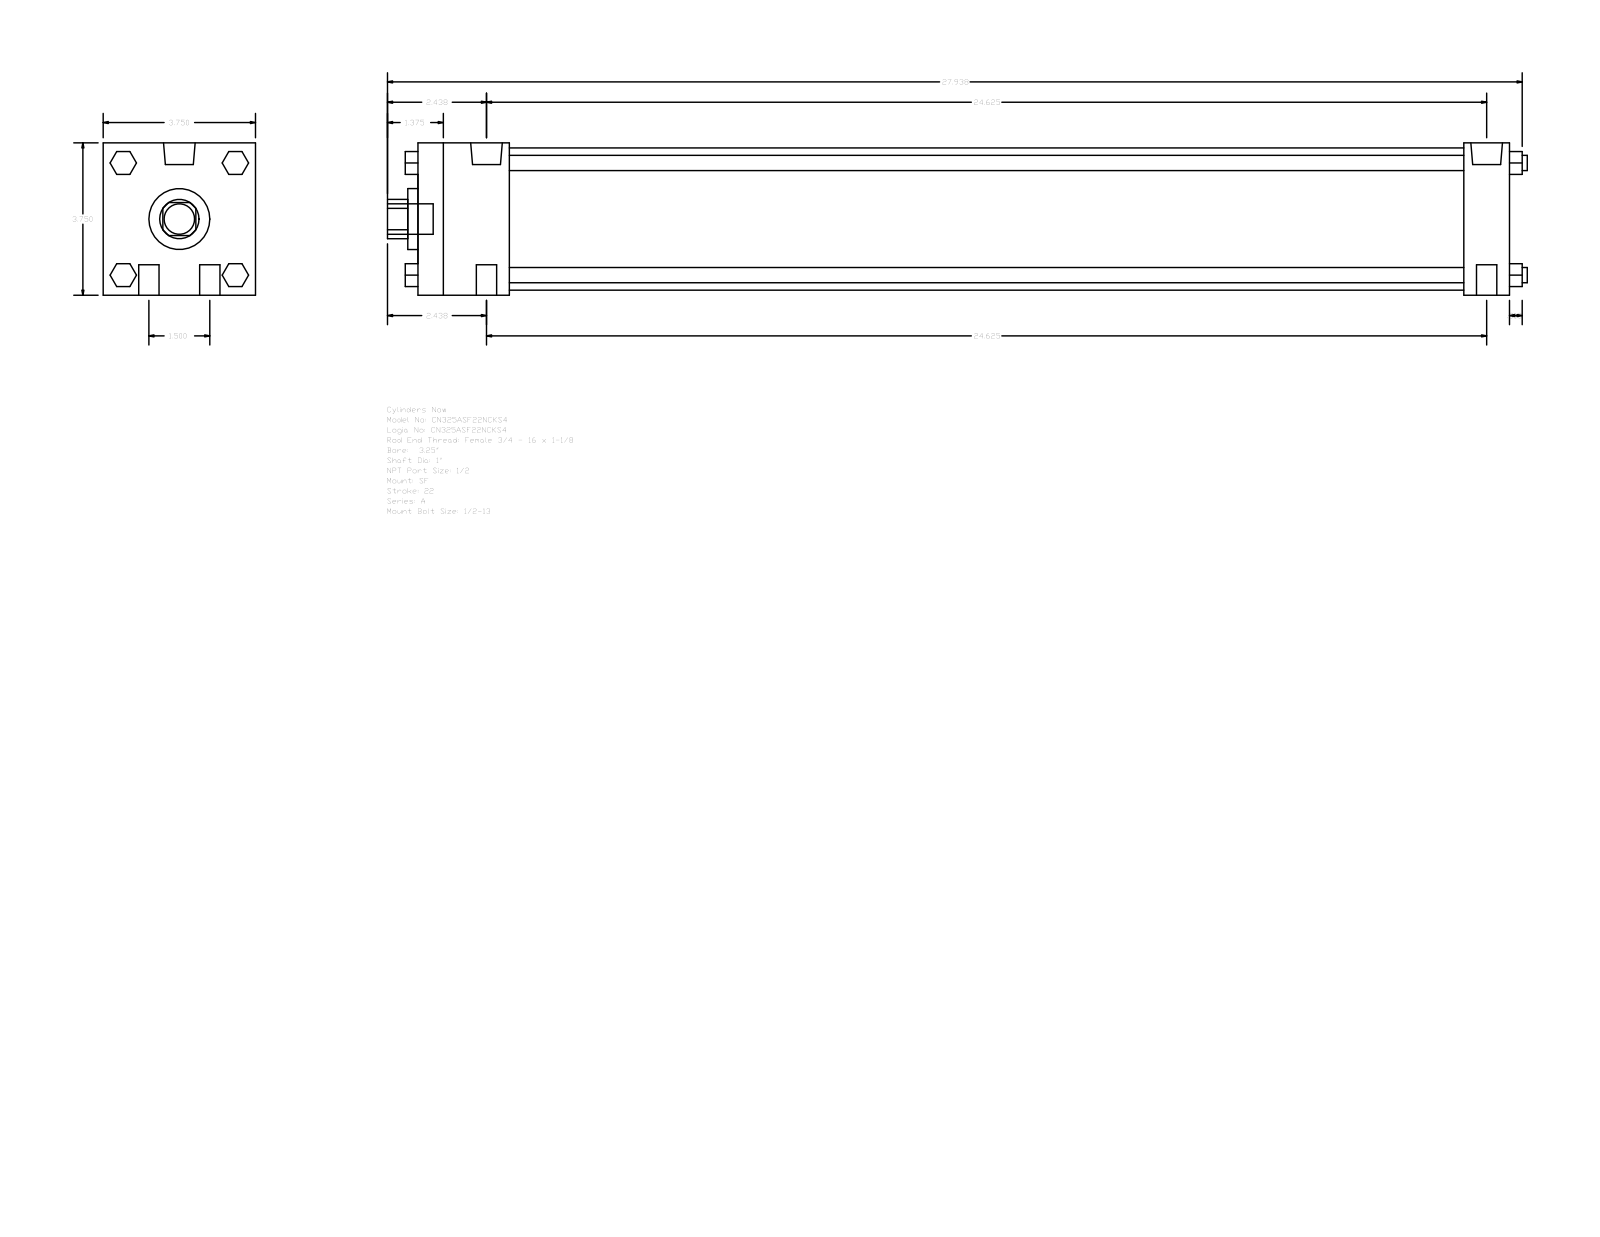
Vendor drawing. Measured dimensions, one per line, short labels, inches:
name: A_SF__0325_1
written by: GSSL Pune (CONFIG_CONTROL_DESIGN)
unit: in
bodies: 0 solids, 124 faces (94 planar, 30 cylindrical, 0 other)
size: 28.063 × 3.75 × 3.75
holes: 1× ⌀1, 1× ⌀1.5, 1× ⌀3.5
bosses: 4× ⌀0.5, 4× ⌀0.375, 2× ⌀0.778, 2× ⌀0.344, 1× ⌀0.75
rounds: 1× R0.484
face distances: 3.75, 26.875, 1.125, 25.75, 2.25, 23.5, 24.625, 0.562, 1.38, 2.39
